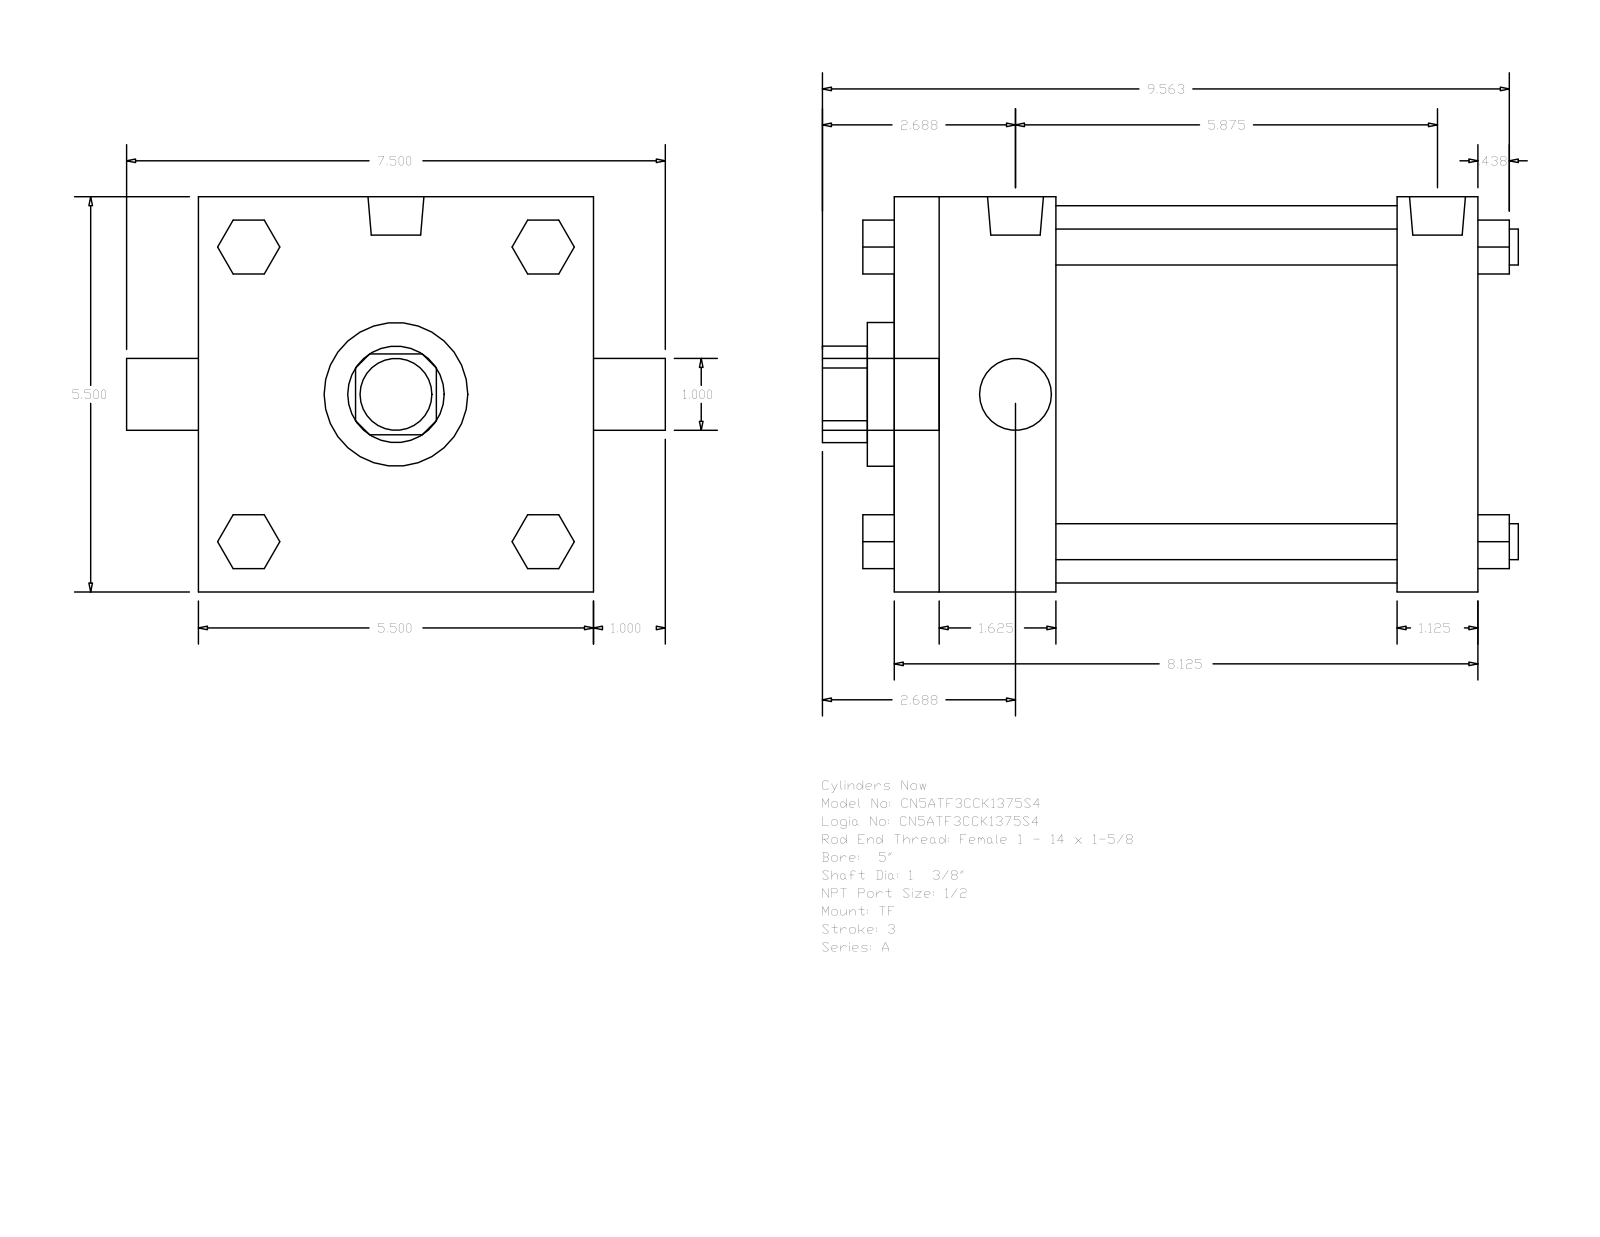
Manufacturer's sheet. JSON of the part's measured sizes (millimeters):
{"part_name": "A_TF__0500_1.375", "step_written_by": "GSSL Pune (CONFIG_CONTROL_DESIGN)", "units": "millimeters", "bodies": {"solids": 0, "faces": 120, "planar": 92, "cylindrical": 28, "other": 0}, "overall_size": [246.06, 190.5, 139.7], "round_holes": [[25.4, 1], [34.92, 1], [50.8, 1], [133.35, 1]], "round_bosses_or_shafts": [[12.7, 4], [8.73, 3], [19.77, 2], [25.4, 1]], "partial_cylinders_radius": [[17.06, 1]], "face_to_face_distances": [139.7, 206.38, 28.58, 177.8, 57.15, 120.65, 149.23, 19.05, 52.07, 90.18]}
